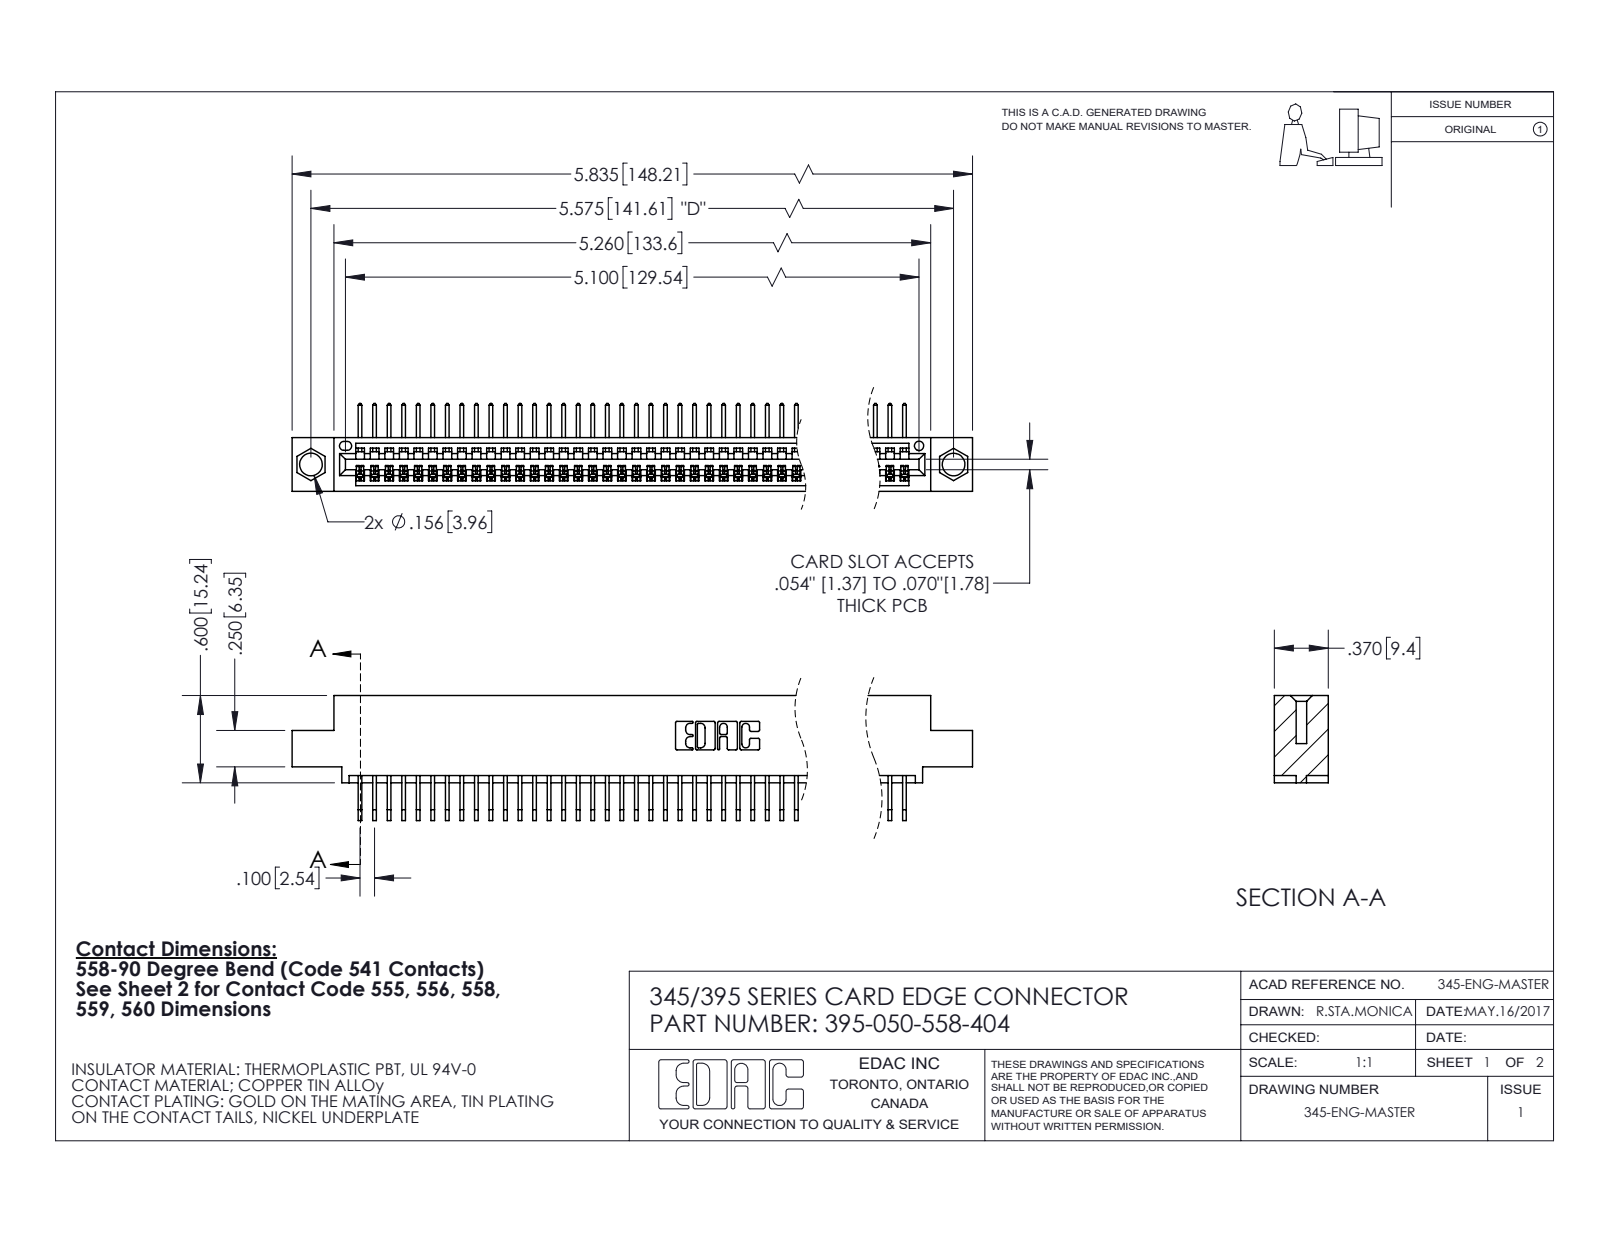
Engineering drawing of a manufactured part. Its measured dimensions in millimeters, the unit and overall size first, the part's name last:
Units: millimetres
Overall size (bounding box): 148.2 × 21.8 × 15.4
Round holes (diameter × count): ⌀4 ×2, ⌀1.6 ×1
Partial cylindrical surfaces — rounded edges, fillets, slot ends (radius × count): R0.2 ×100, R0.3 ×22, R0.2 ×6, R0.8 ×6, R0.7 ×3, R0.8 ×2, R1 ×2, R0.4 ×1
Main face-to-face distances: 1.8, 7.6, 9.4, 5.1, 2.5, 6.9, 0.6, 5.7, 3.8, 1.8
Hole centre spacings: 6.9, 135.6, 141.6
Volume: 14 100 mm³ · Surface area: 19 790 mm²
Bodies: 51 solids, 3144 faces (2198 planar, 946 cylindrical, 0 other)
Part name (STEP PRODUCT): 395-050-558-404; 345-292-001_558 Tail - 2; 345 Part_0.110 Offset - 0.156 Dia-TI
STEP written by: SolidWorks 2020 (CONFIG_CONTROL_DESIGN)
